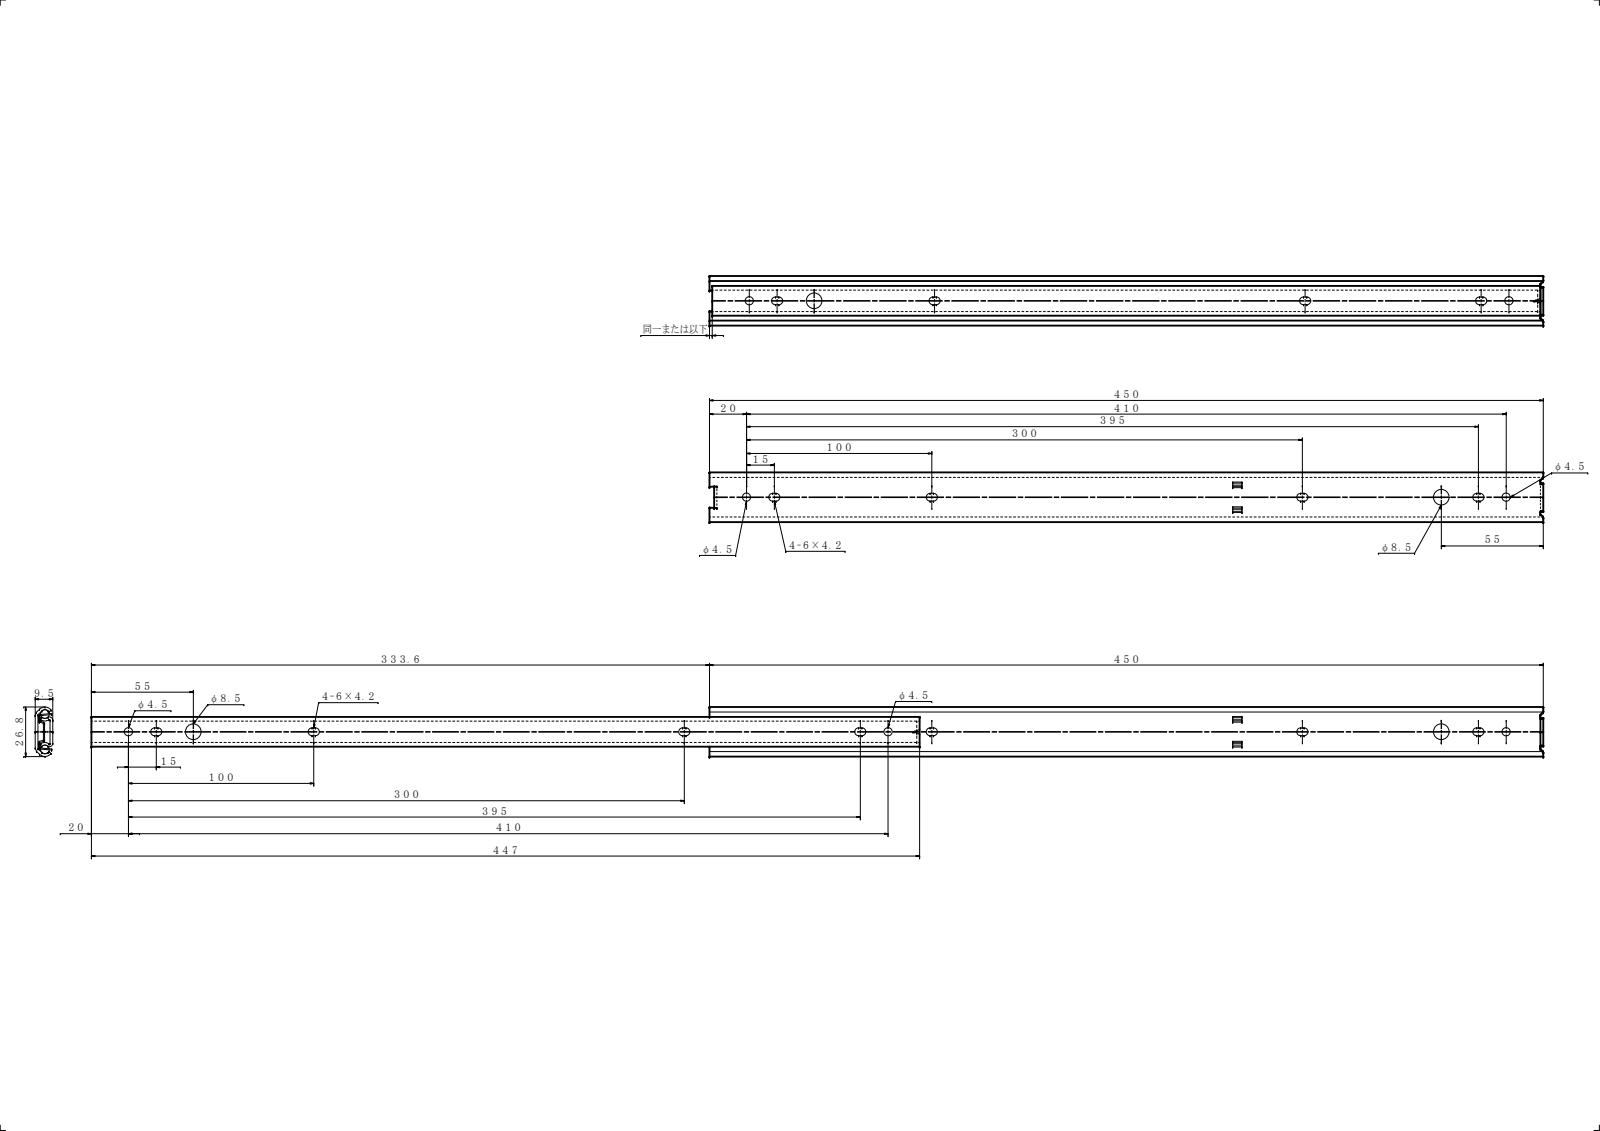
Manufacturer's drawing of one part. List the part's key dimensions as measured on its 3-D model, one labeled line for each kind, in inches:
Part name (STEP PRODUCT): U2721-450 OM; U2721-450 IM; U2721_450
STEP written by: SolidWorks 2019 (CONFIG_CONTROL_DESIGN)
Units: inches
Bodies: 2 solids, 134 faces (61 planar, 73 cylindrical, 0 other)
Overall size (bounding box): 30.85 × 1.055 × 0.374
Volume: 2.527 in³ · Surface area: 91.15 in²
Round holes (diameter × count): ⌀0.177 ×4, ⌀0.335 ×2
Partial cylindrical surfaces — rounded edges, fillets, slot ends (radius × count): R0.083 ×16, R0.079 ×10, R0.039 ×5, R0.02 ×4, R0.007 ×2, R0.051 ×2, R0.066 ×2, R0.094 ×2
Main face-to-face distances: 0.059, 0.315, 0.374, 0.256, 13.252, 13.193, 17.56, 4.308, 13.311, 17.619
Hole centre spacings: 1.378, 11.756, 13.134, 14.764, 16.142, 27.898, 3.008, 26.52
